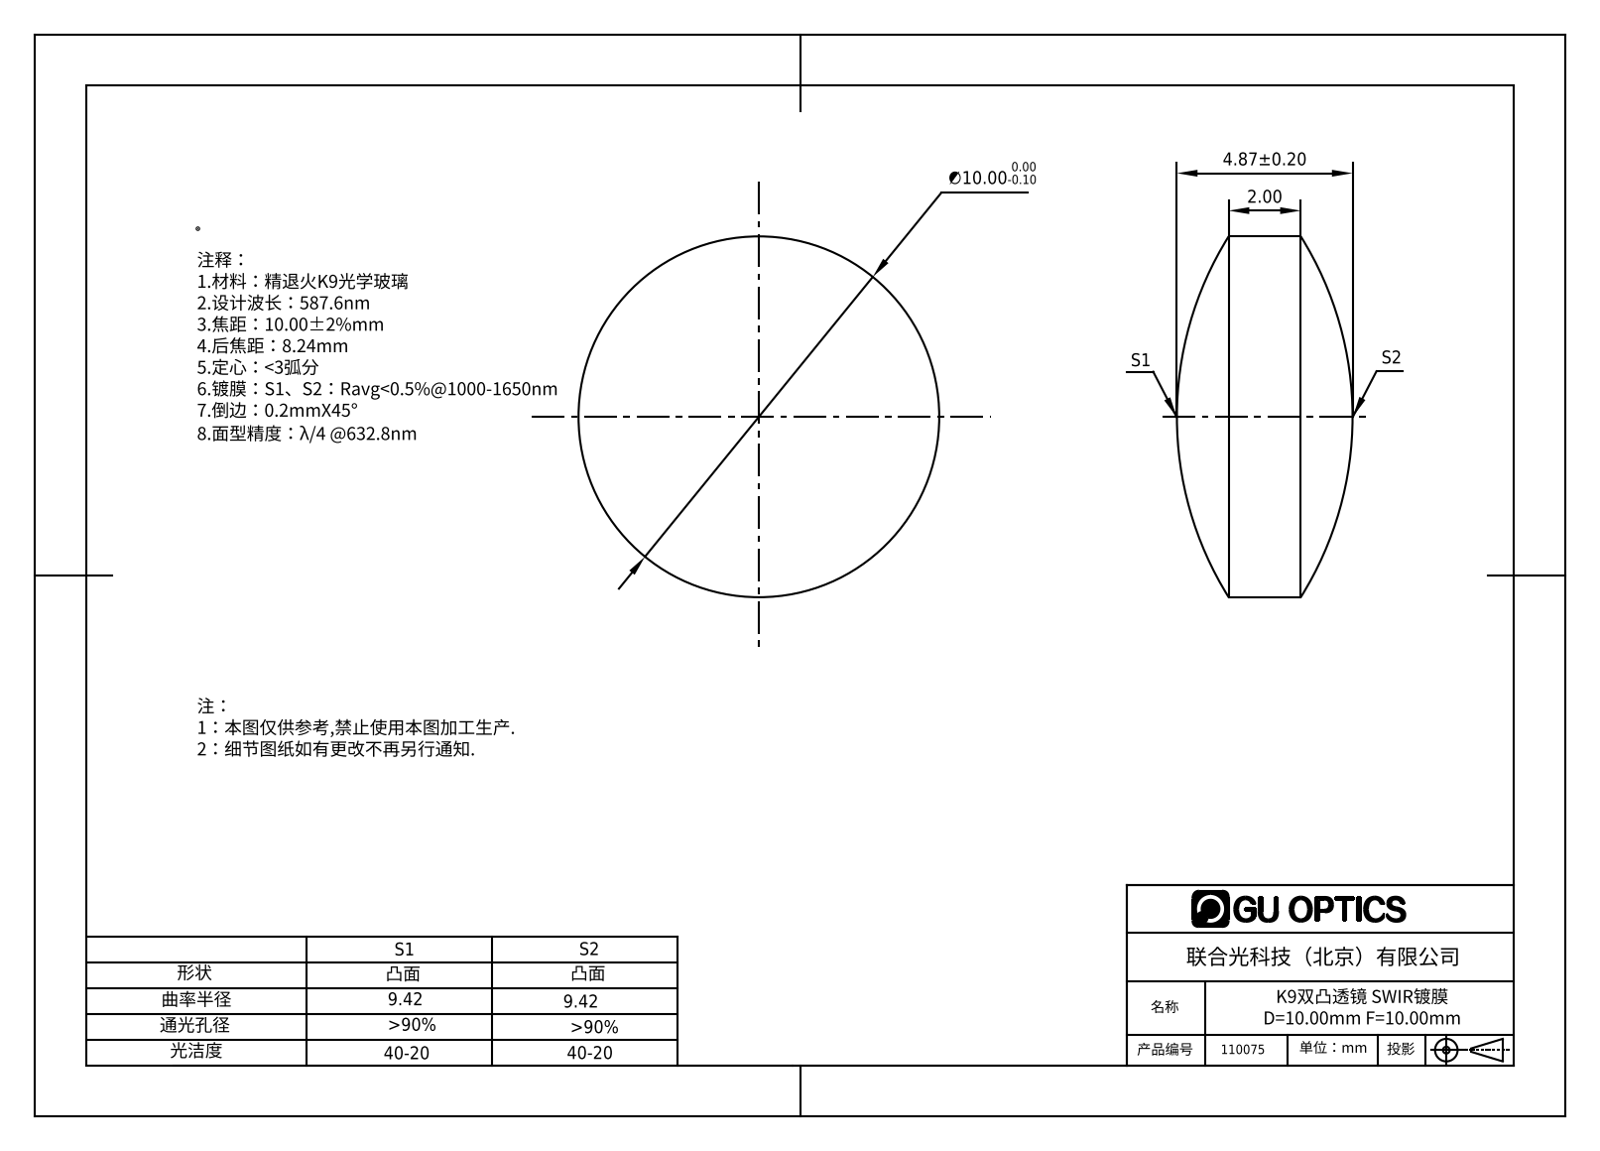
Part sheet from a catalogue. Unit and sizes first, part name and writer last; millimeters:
Units: millimetres
Overall size (bounding box): 10 × 10 × 4.87
Round bosses / shafts (diameter × count): ⌀10 ×1
Volume: 273 mm³ · Surface area: 233 mm²
Bodies: 1 solid, 6 faces (0 planar, 2 cylindrical, 4 other)
Part name (STEP PRODUCT): 1100009
STEP written by: SolidWorks 2016 (CONFIG_CONTROL_DESIGN)
